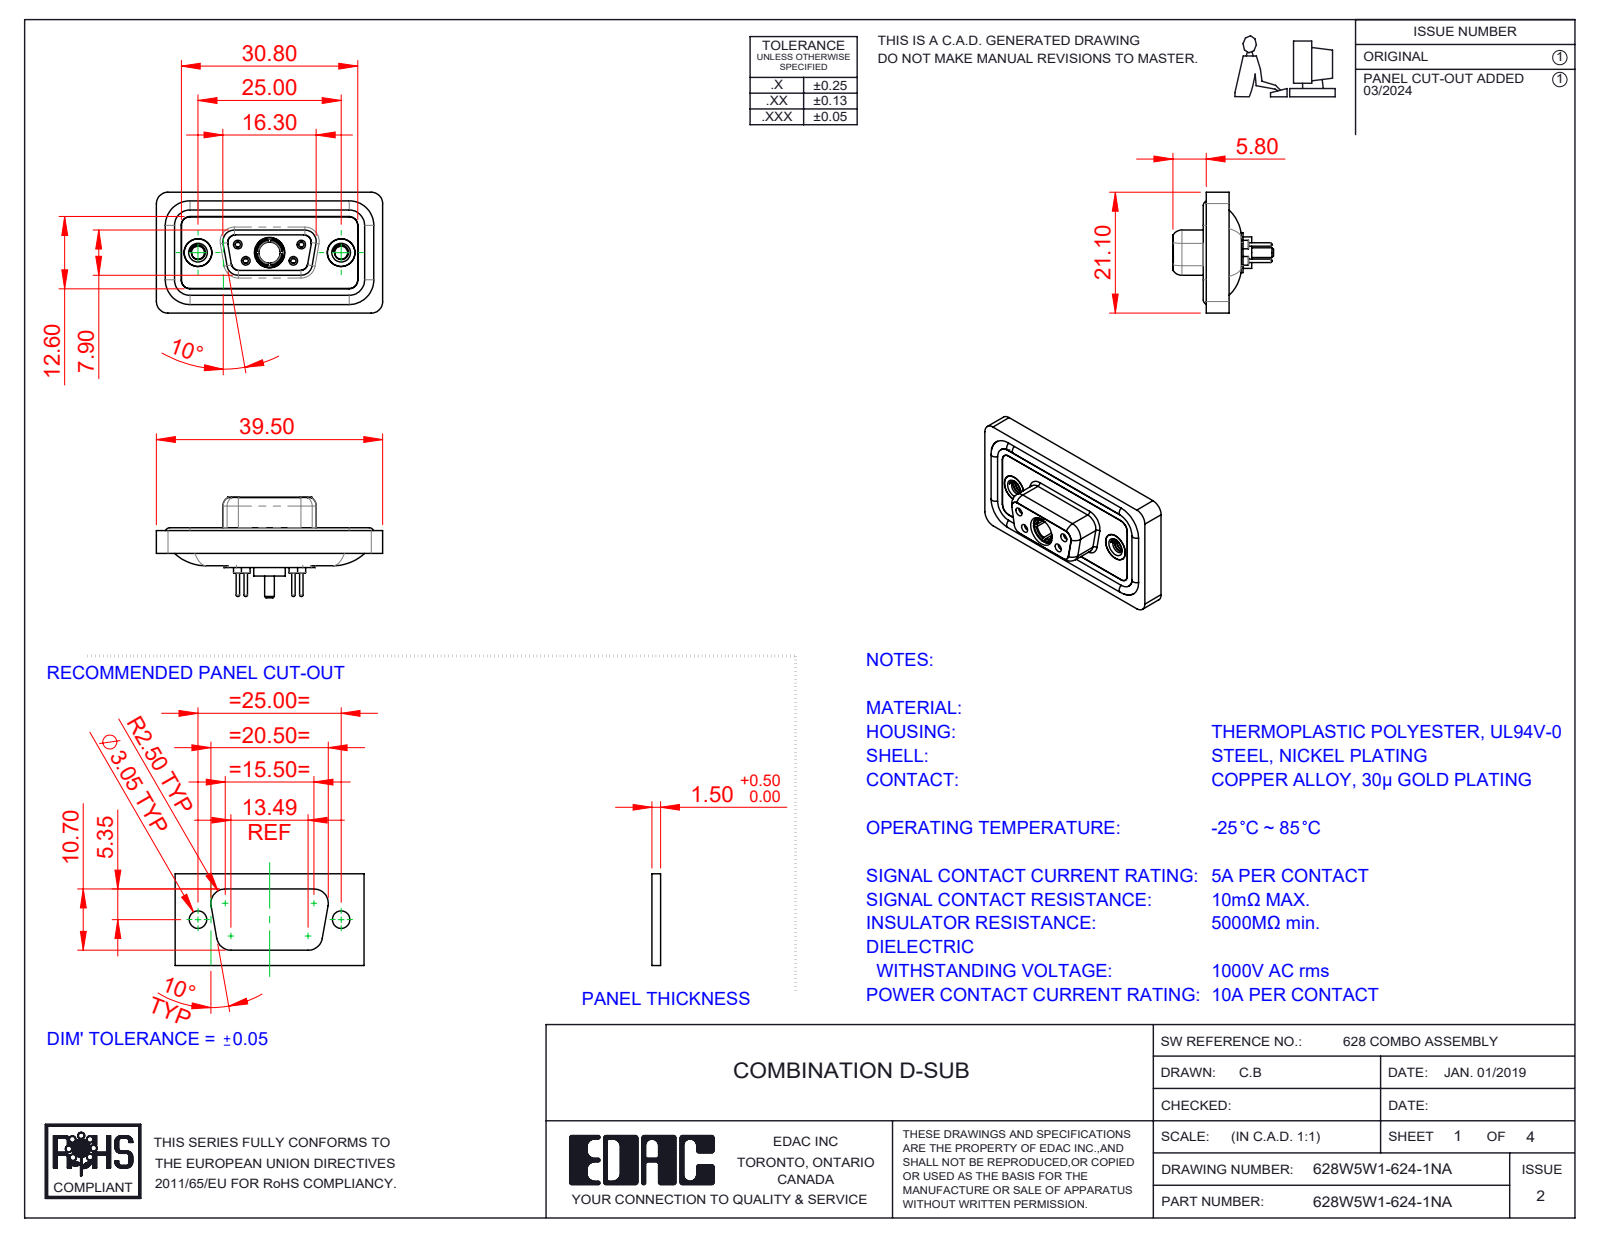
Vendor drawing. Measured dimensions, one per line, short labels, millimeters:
name: 628Combo Shell Rear_09 Contacts; Power Socket_10A S; 628Combo Housing_5W1; 628W5W1-624-1NA (+5 more)
written by: SolidWorks 2023 (CONFIG_CONTROL_DESIGN)
unit: mm
bodies: 13 solids, 678 faces (194 planar, 289 cylindrical, 195 other)
size: 39.5 × 21.1 × 17.55
volume: 4 754 mm³; area: 7 620 mm²
holes: 4× ⌀0.9, 4× ⌀1.1, 4× ⌀1.5, 4× ⌀2, 3× ⌀4.85, 2× ⌀1.6, 2× ⌀1.7, 2× ⌀2.26, 2× ⌀4, 2× ⌀4.05, 2× ⌀5, 1× ⌀3.7
bosses: 6× ⌀1.6, 4× ⌀2.2, 4× ⌀0.6, 2× ⌀4.95, 2× ⌀4.8, 1× ⌀5.5, 1× ⌀5.2, 1× ⌀4.96
rounds: 22× R1.5, 18× R2, 8× R1.35, 8× R1.6, 4× R0.25, 4× R0.5, 4× R0.6, 4× R0.65
face distances: 0.4, 2.9, 1.8, 1.1, 1.6, 0.5, 5.65, 7.45, 5.35, 6.6
hole spacings: 3.16, 5.72, 7.1, 12.5, 18.1, 4.39, 4.4, 8.31
